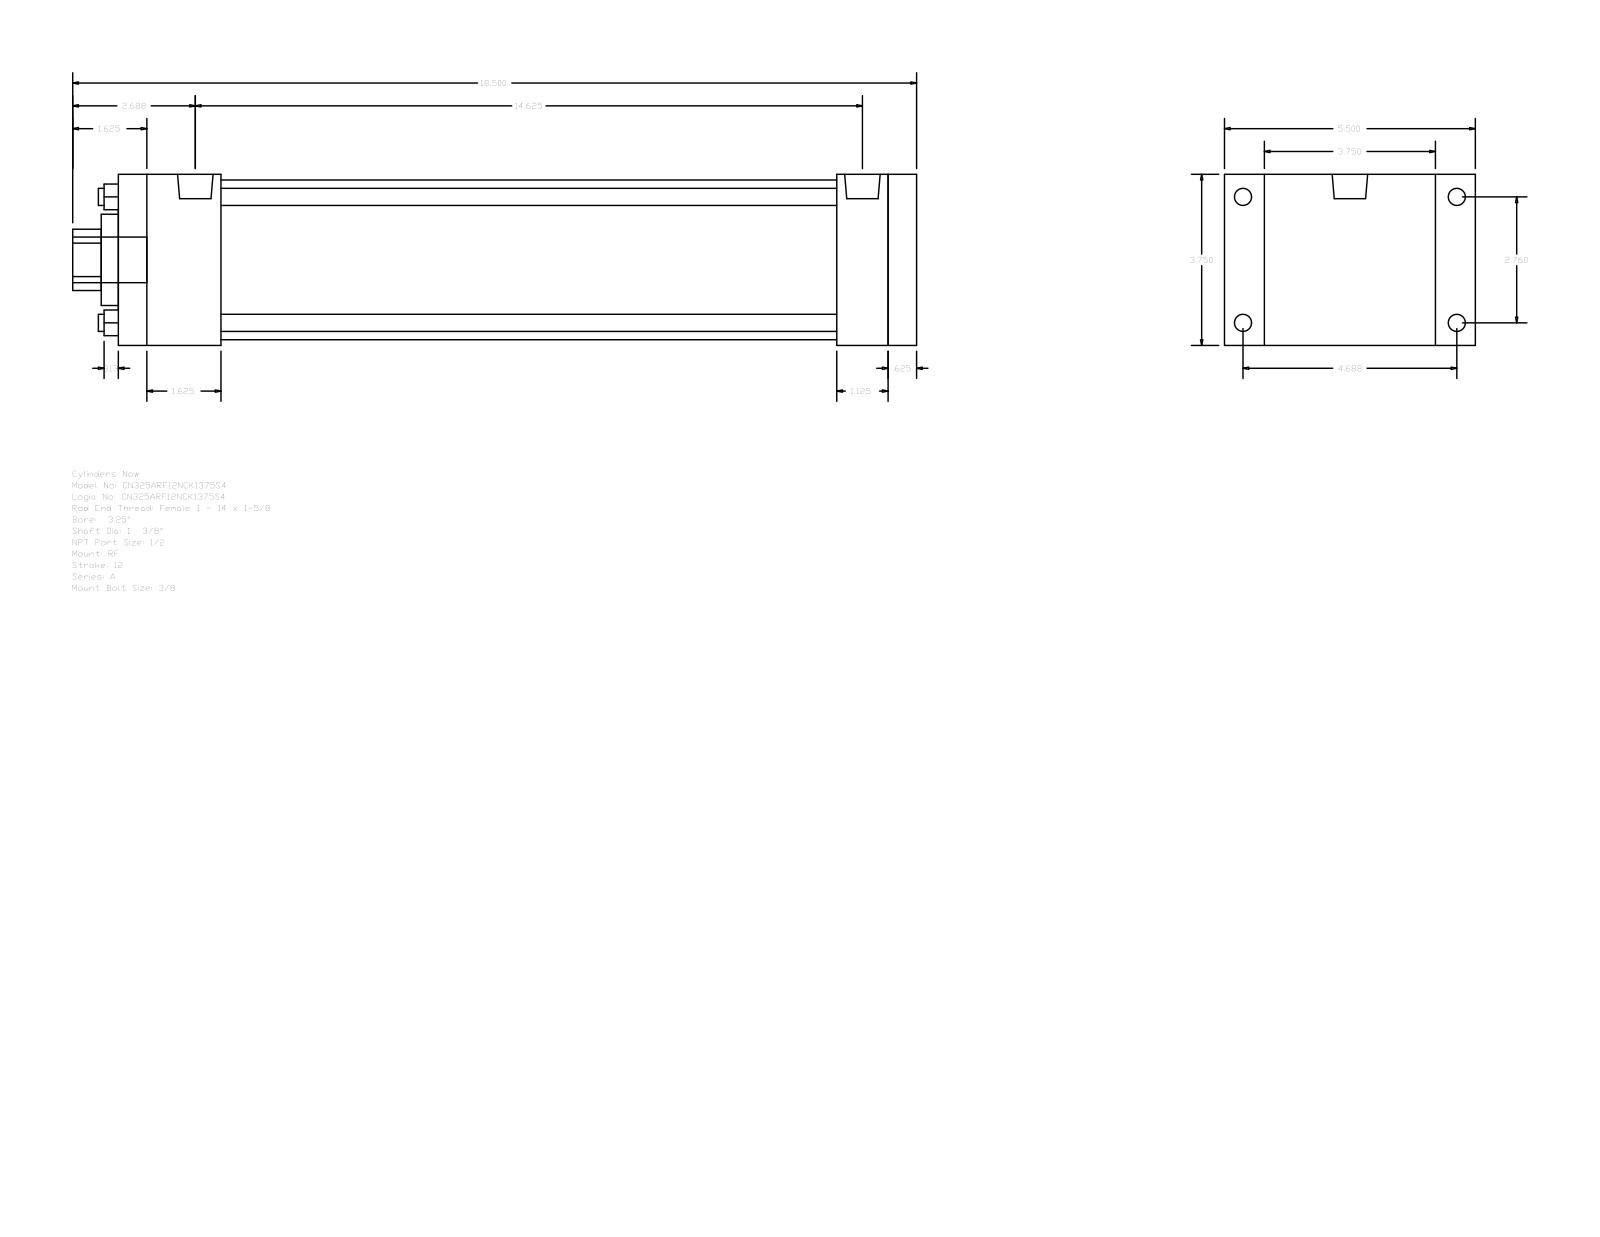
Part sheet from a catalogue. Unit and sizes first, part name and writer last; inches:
Units: inches
Overall size (bounding box): 18.5 × 5.5 × 3.75
Round holes (diameter × count): ⌀0.375 ×4, ⌀1.375 ×1, ⌀2 ×1, ⌀3.5 ×1
Round bosses / shafts (diameter × count): ⌀0.375 ×4, ⌀0.344 ×4, ⌀0.778 ×2, ⌀1 ×1
Partial cylindrical surfaces — rounded edges, fillets, slot ends (radius × count): R0.672 ×1
Main face-to-face distances: 3.75, 17.5, 0.625, 16.875, 0.875, 4.625, 1.125, 15.75, 1.75, 2.25
Hole centre spacings: 1.952, 2.76, 3.903
Bodies: 0 solids, 92 faces (64 planar, 28 cylindrical, 0 other)
Part name (STEP PRODUCT): A_RF__0325_1.375
STEP written by: GSSL Pune (CONFIG_CONTROL_DESIGN)
